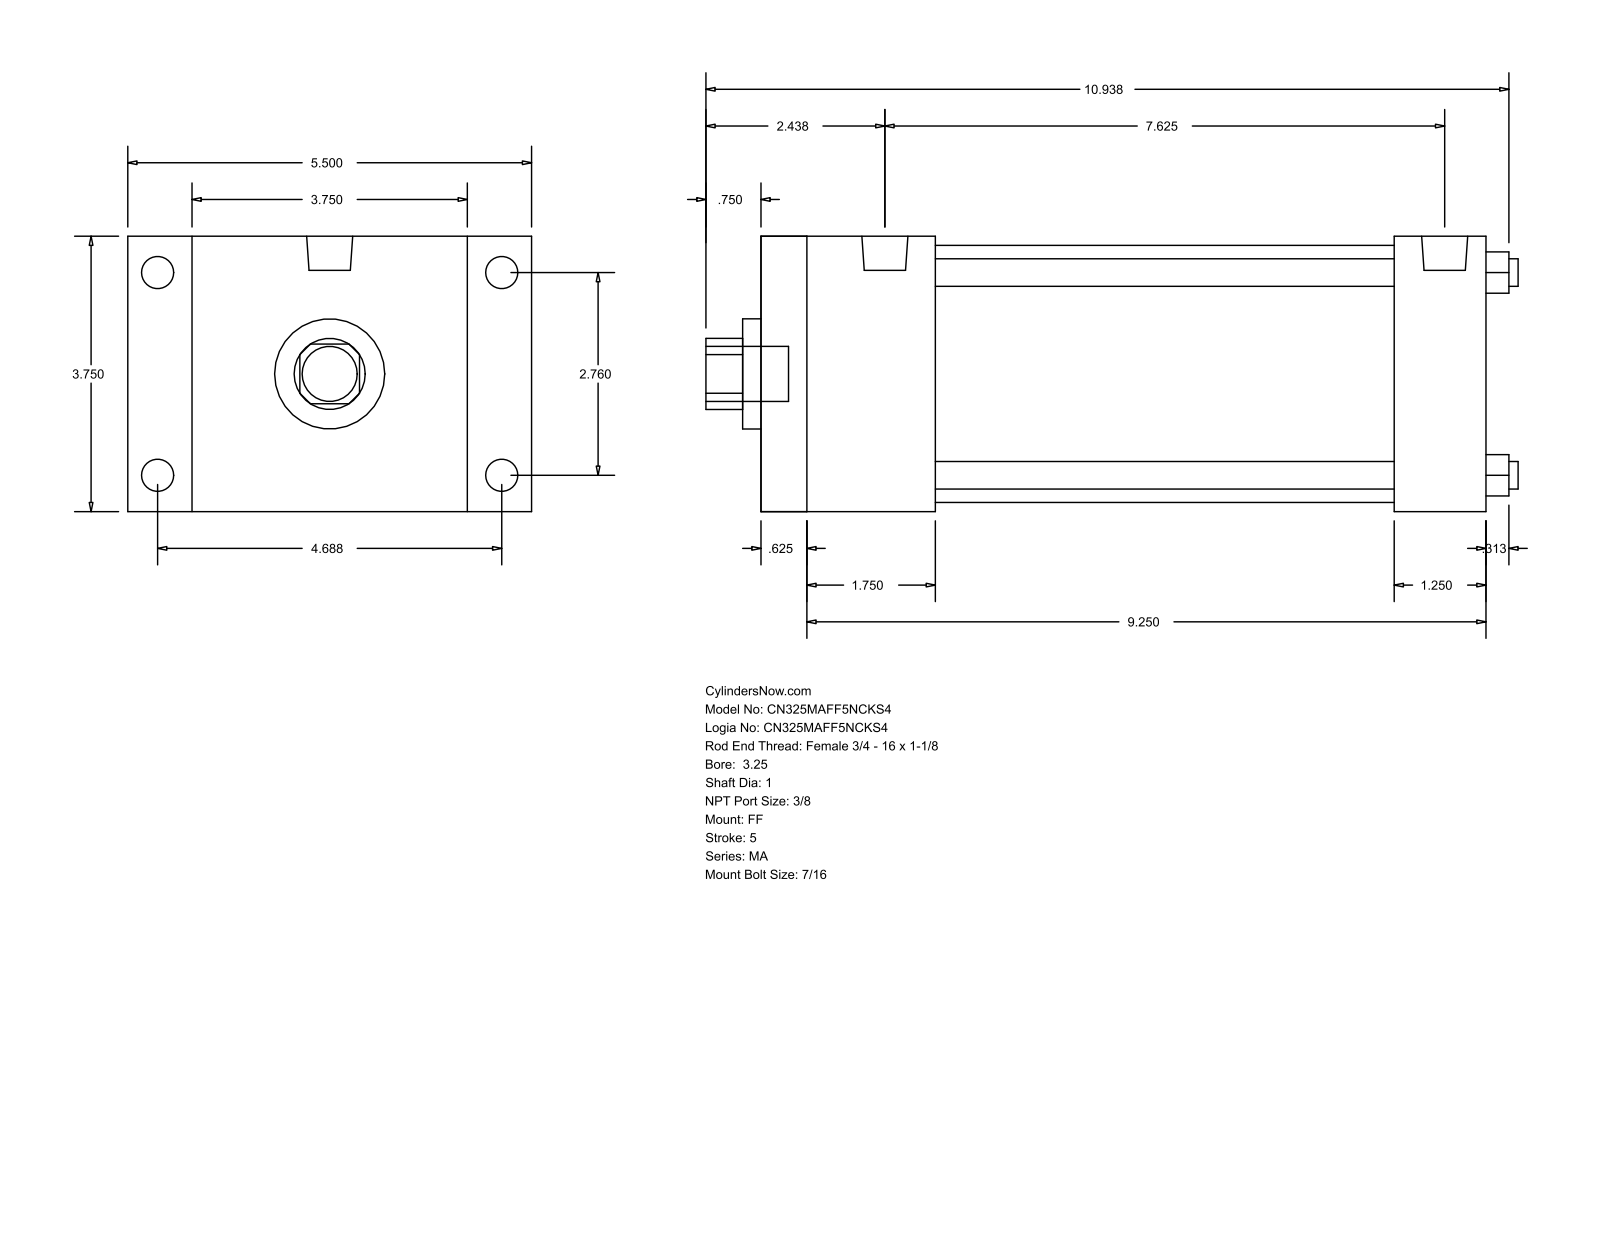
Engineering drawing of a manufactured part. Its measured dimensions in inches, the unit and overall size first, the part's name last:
Units: inches
Overall size (bounding box): 11.063 × 5.5 × 3.75
Round holes (diameter × count): ⌀0.375 ×4, ⌀1 ×1, ⌀1.5 ×1, ⌀3.5 ×1
Round bosses / shafts (diameter × count): ⌀0.437 ×8, ⌀0.627 ×2, ⌀0.75 ×1
Partial cylindrical surfaces — rounded edges, fillets, slot ends (radius × count): R0.484 ×1
Main face-to-face distances: 3.75, 9.875, 0.625, 9.25, 0.875, 4.625, 2.375, 8.625, 1.75, 8
Hole centre spacings: 1.952, 2.76, 3.903
Bodies: 0 solids, 92 faces (64 planar, 28 cylindrical, 0 other)
Part name (STEP PRODUCT): MA_FF__0325_1
STEP written by: GSSL Pune (CONFIG_CONTROL_DESIGN)
